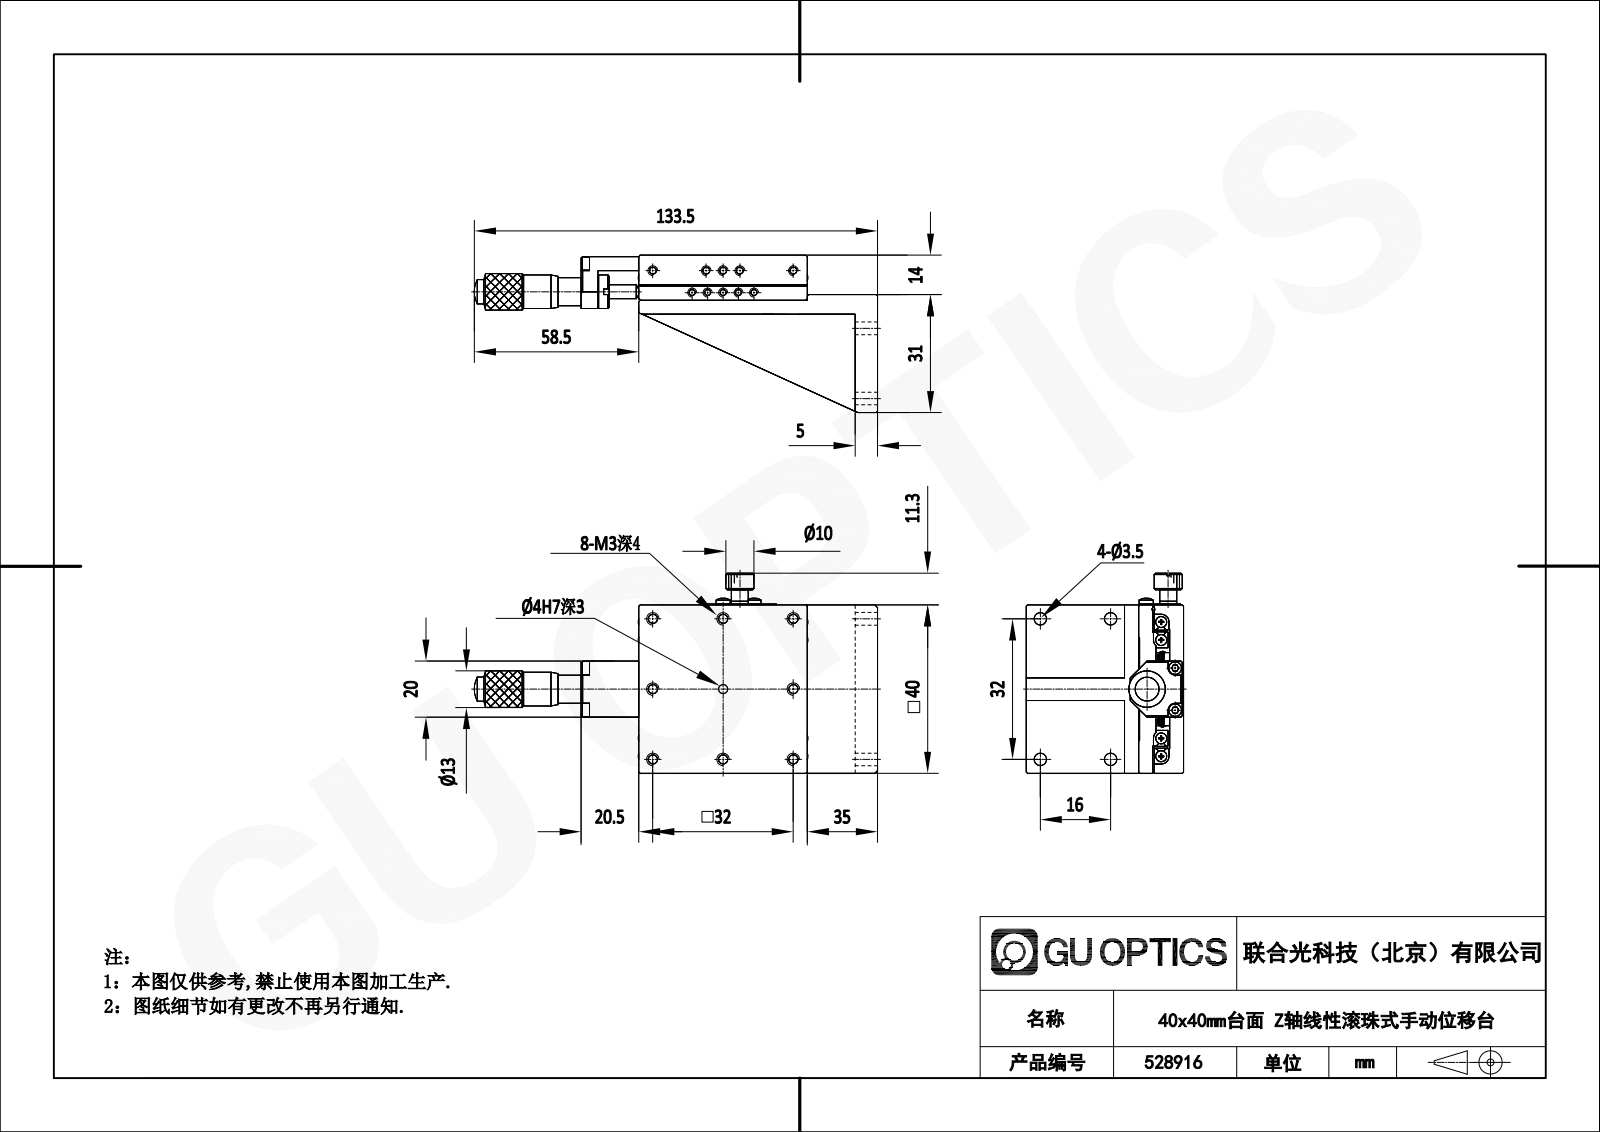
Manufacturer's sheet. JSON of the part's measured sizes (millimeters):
{"part_name": "528916", "step_written_by": "SolidWorks 2020 (CONFIG_CONTROL_DESIGN)", "units": "millimeters", "bodies": {"solids": 4, "faces": 2343, "planar": 284, "cylindrical": 484, "other": 1575}, "overall_size": [135.51, 51.3, 45], "volume_mm3": 54609, "surface_area_mm2": 29346, "round_holes": [[2.46, 8], [3.5, 8], [6, 4], [2.01, 2], [2.01, 2], [2.85, 2], [4, 1], [5, 1], [9, 1]], "round_bosses_or_shafts": [[4.5, 8], [13.03, 1], [12.03, 1], [12, 1], [10.5, 1], [7, 1], [3, 1]], "partial_cylinders_radius": [[0.1, 24], [2, 4], [1.4, 2], [1.75, 2], [2.5, 2], [3, 2], [1, 1]], "face_to_face_distances": [5, 16, 5.5, 10.5, 15.5, 24, 40, 14, 0.5, 2], "hole_center_spacings": [16, 35.78, 22.63, 32, 20, 32.25, 45.25]}
